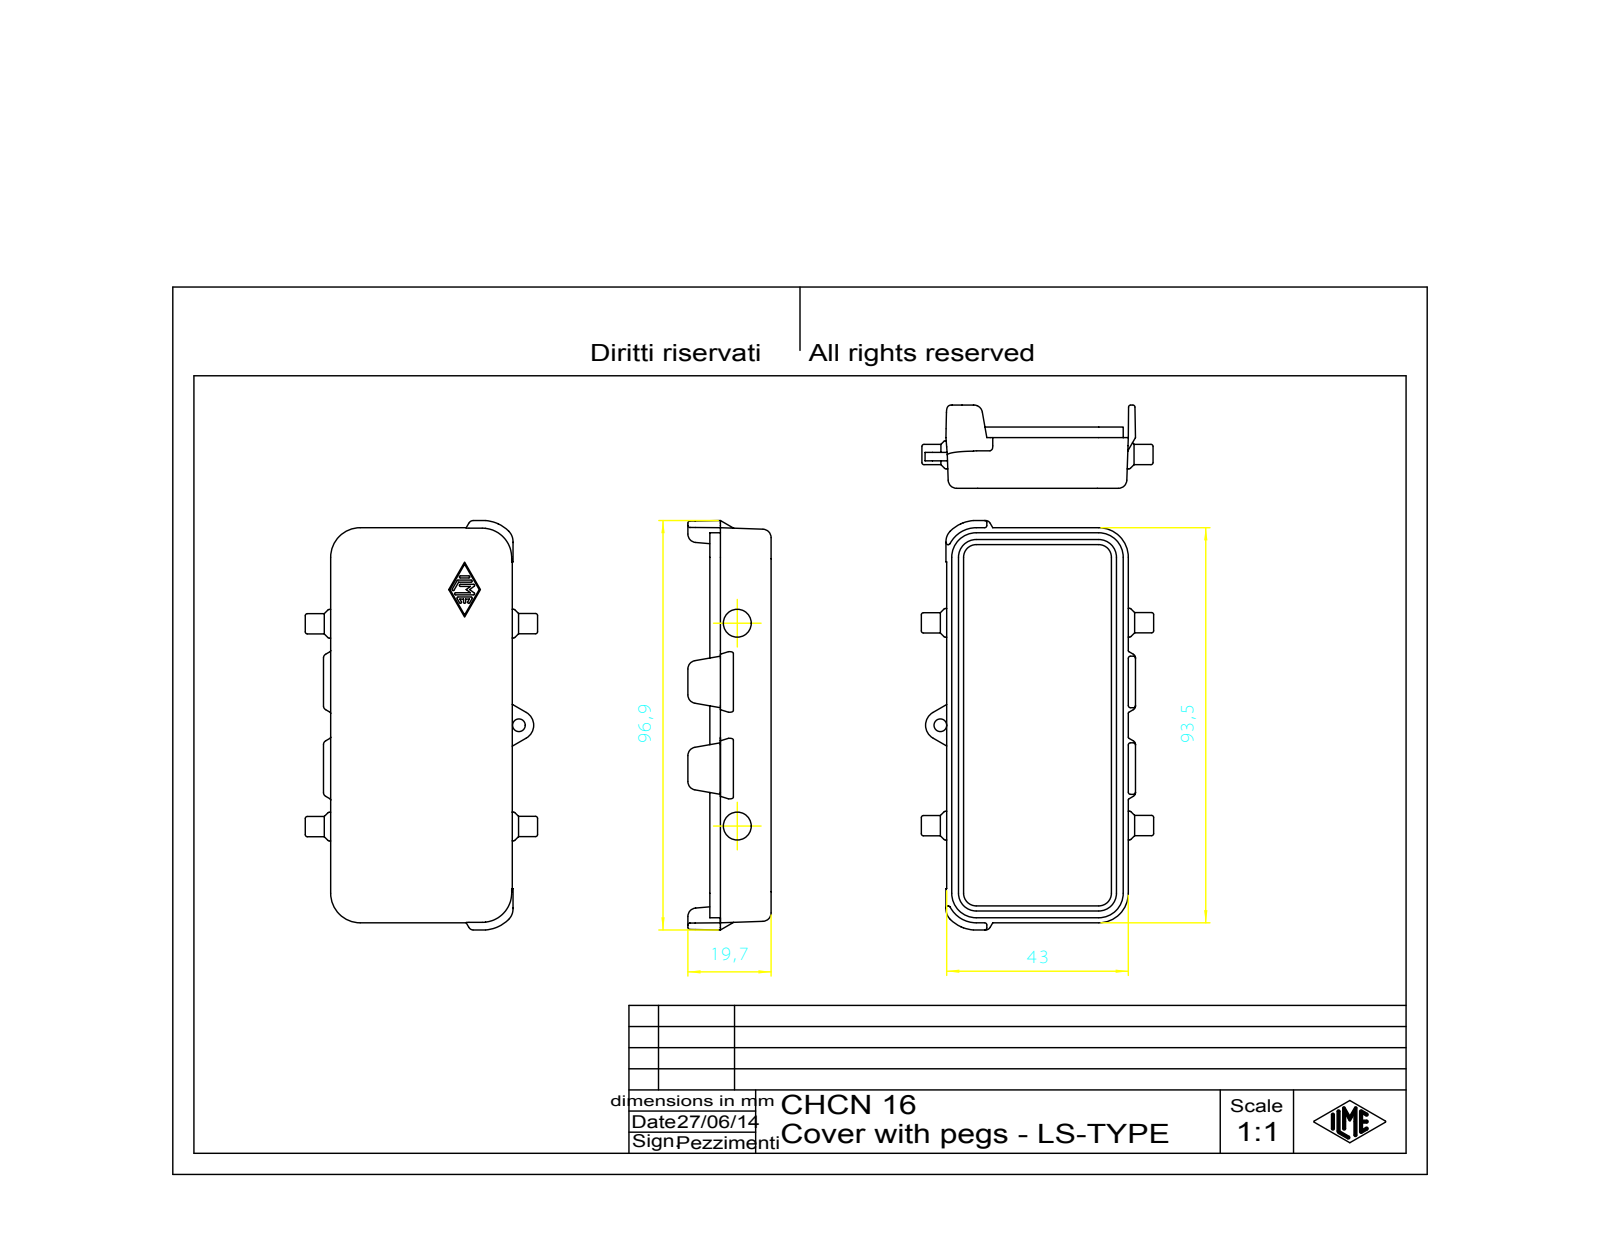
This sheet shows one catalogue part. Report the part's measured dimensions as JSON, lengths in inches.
{"part_name": "CHCN_16", "step_written_by": "CoCreate Modeling 16.00A 16-Aug-2008 (C) Parametric Technology GmbH (AUTOMOTIVE_DESIGN)", "units": "inches", "bodies": {"solids": 1, "faces": 222, "planar": 119, "cylindrical": 83, "other": 20}, "overall_size": [6.074, 3.681, 0.551], "volume_in3": 1.424, "surface_area_in2": 22.25, "round_holes": [[0.098, 1], [0.157, 1]], "round_bosses_or_shafts": [[0.039, 4], [0.197, 2], [0.276, 1]], "partial_cylinders_radius": [[0.024, 14], [0.079, 8], [0.028, 6], [0.039, 4], [0.169, 4], [0.03, 2], [0.118, 2], [0.069, 1]], "face_to_face_distances": [0.118, 0.177, 1.516, 0.354, 0.472, 1.693, 1.339, 3.504, 3.681, 3.327], "hole_center_spacings": [3.938]}
